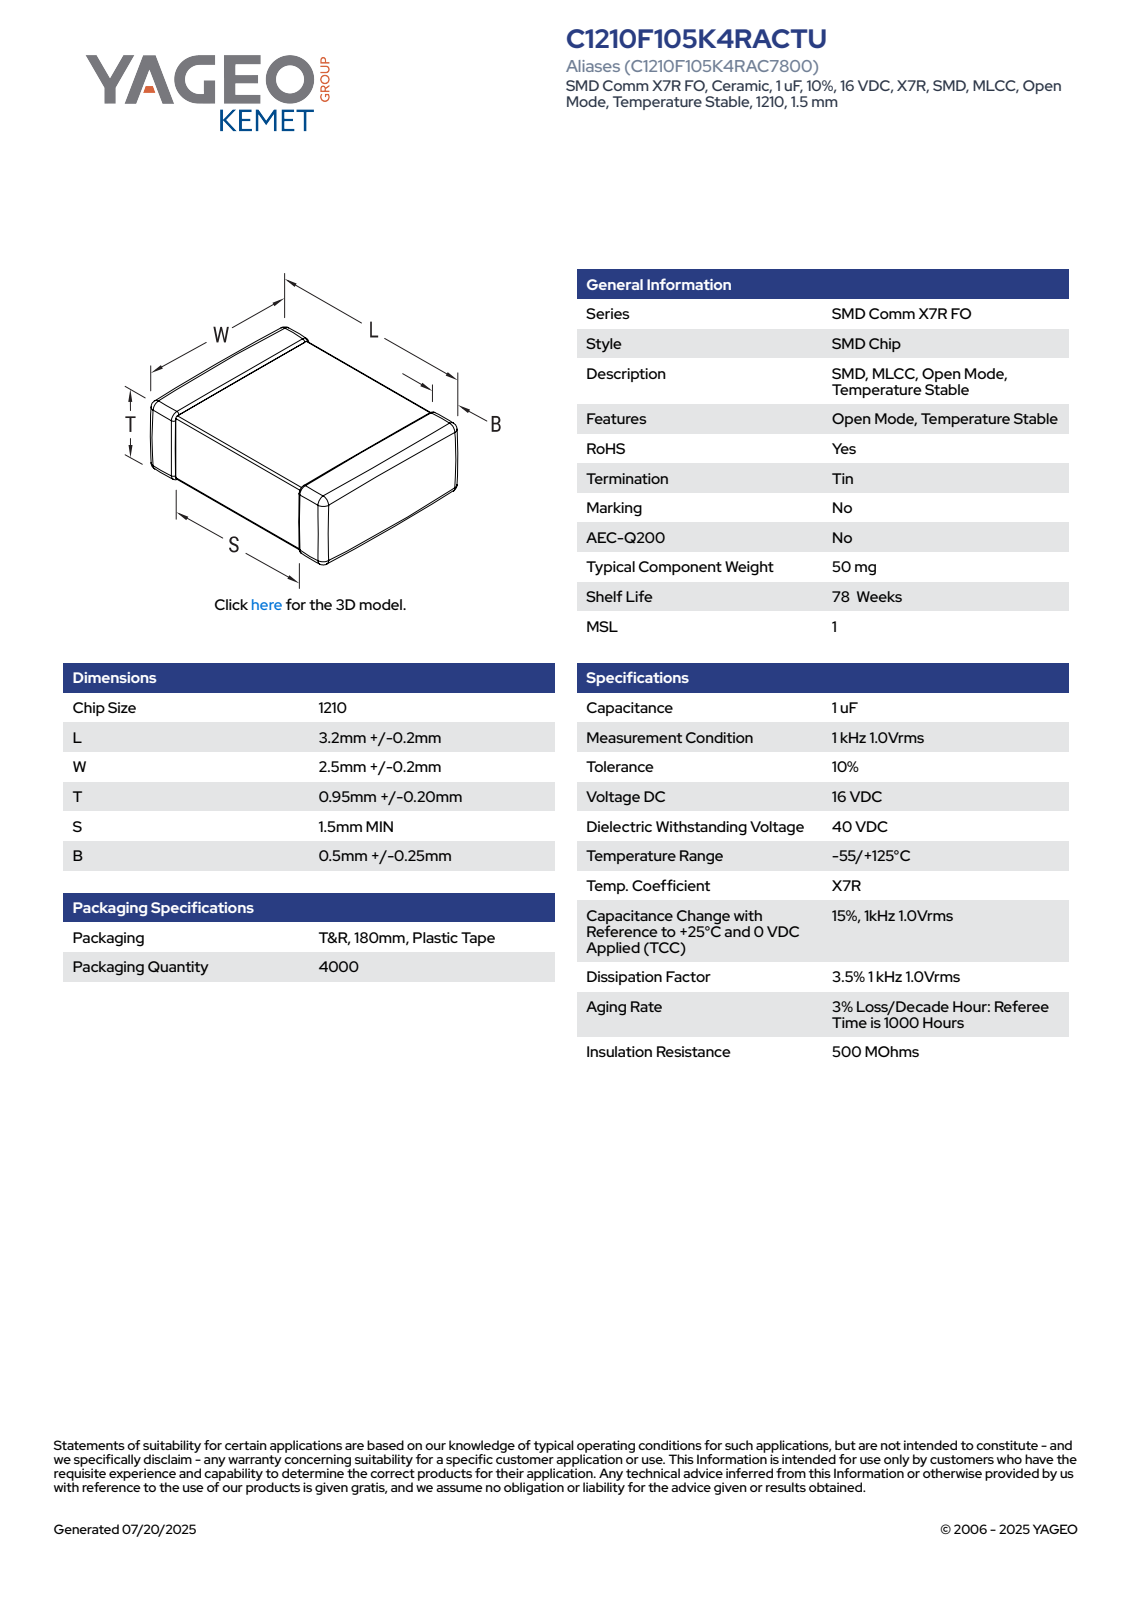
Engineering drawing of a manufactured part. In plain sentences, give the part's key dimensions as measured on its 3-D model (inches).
The part is named "CCS_CCSTD_1210_L3.4W2.7T1.15B0.5". Its 3-D file was written by "SolidWorks 2021 (AUTOMOTIVE_DESIGN)". It is 4 solids with 125 faces: 71 planar, 38 cylindrical and 16 other. Overall it measures 0.134 by 0.106 by 0.045 inches. Its volume is 0.001 cubic inches and its surface area 0.05 square inches. The main face-to-face distances are 0.043, 0.041, 0.045, 0.134, 0.104, 0.102, 0.106, 0.043, 0.041, 0.016.
